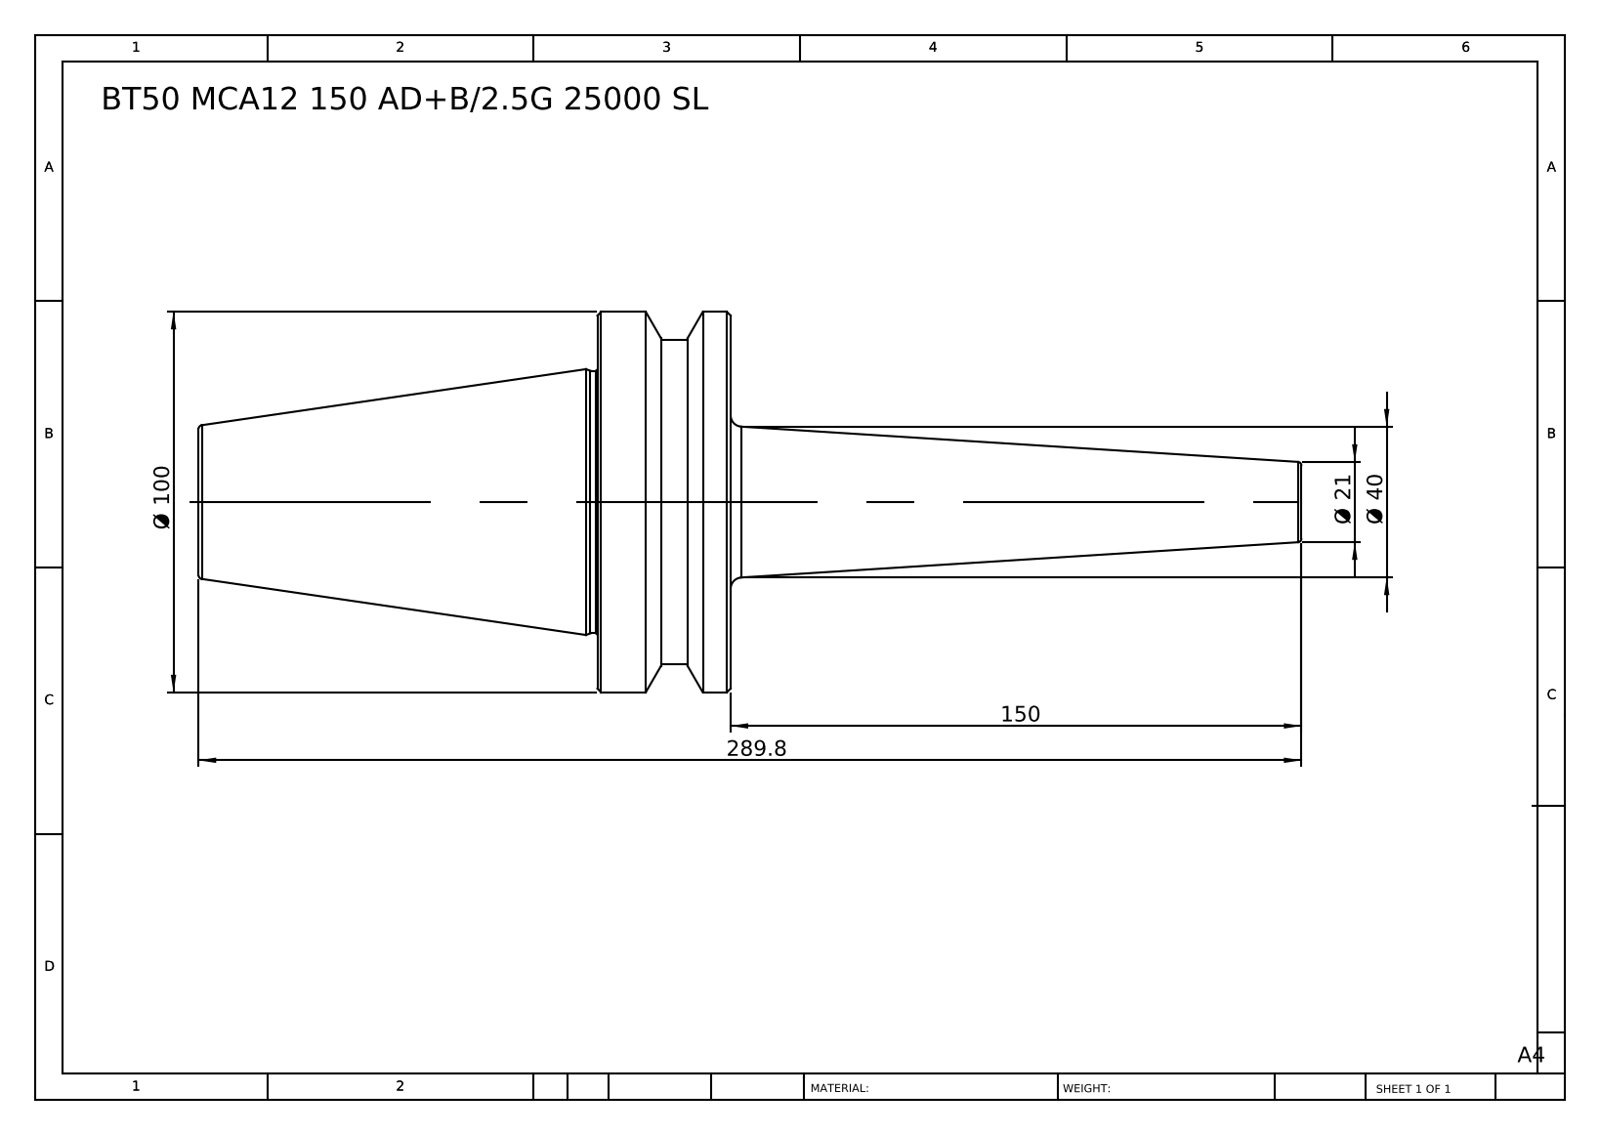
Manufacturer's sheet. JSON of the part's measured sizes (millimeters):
{"part_name": "BT50 MCA12 150 AD+B-2.5G 25000 SL", "step_written_by": "SolidWorks 2014 (CONFIG_CONTROL_DESIGN)", "units": "millimeters", "bodies": {"solids": 1, "faces": 36, "planar": 6, "cylindrical": 8, "other": 22}, "overall_size": [289.8, 100, 100], "volume_mm3": 623391, "surface_area_mm2": 57694, "round_bosses_or_shafts": [[100, 1], [85, 1], [69, 1]], "face_to_face_distances": [35, 139.8, 104.8, 150, 185, 289.8, 161.3, 11.3, 23.7, 128.5]}
